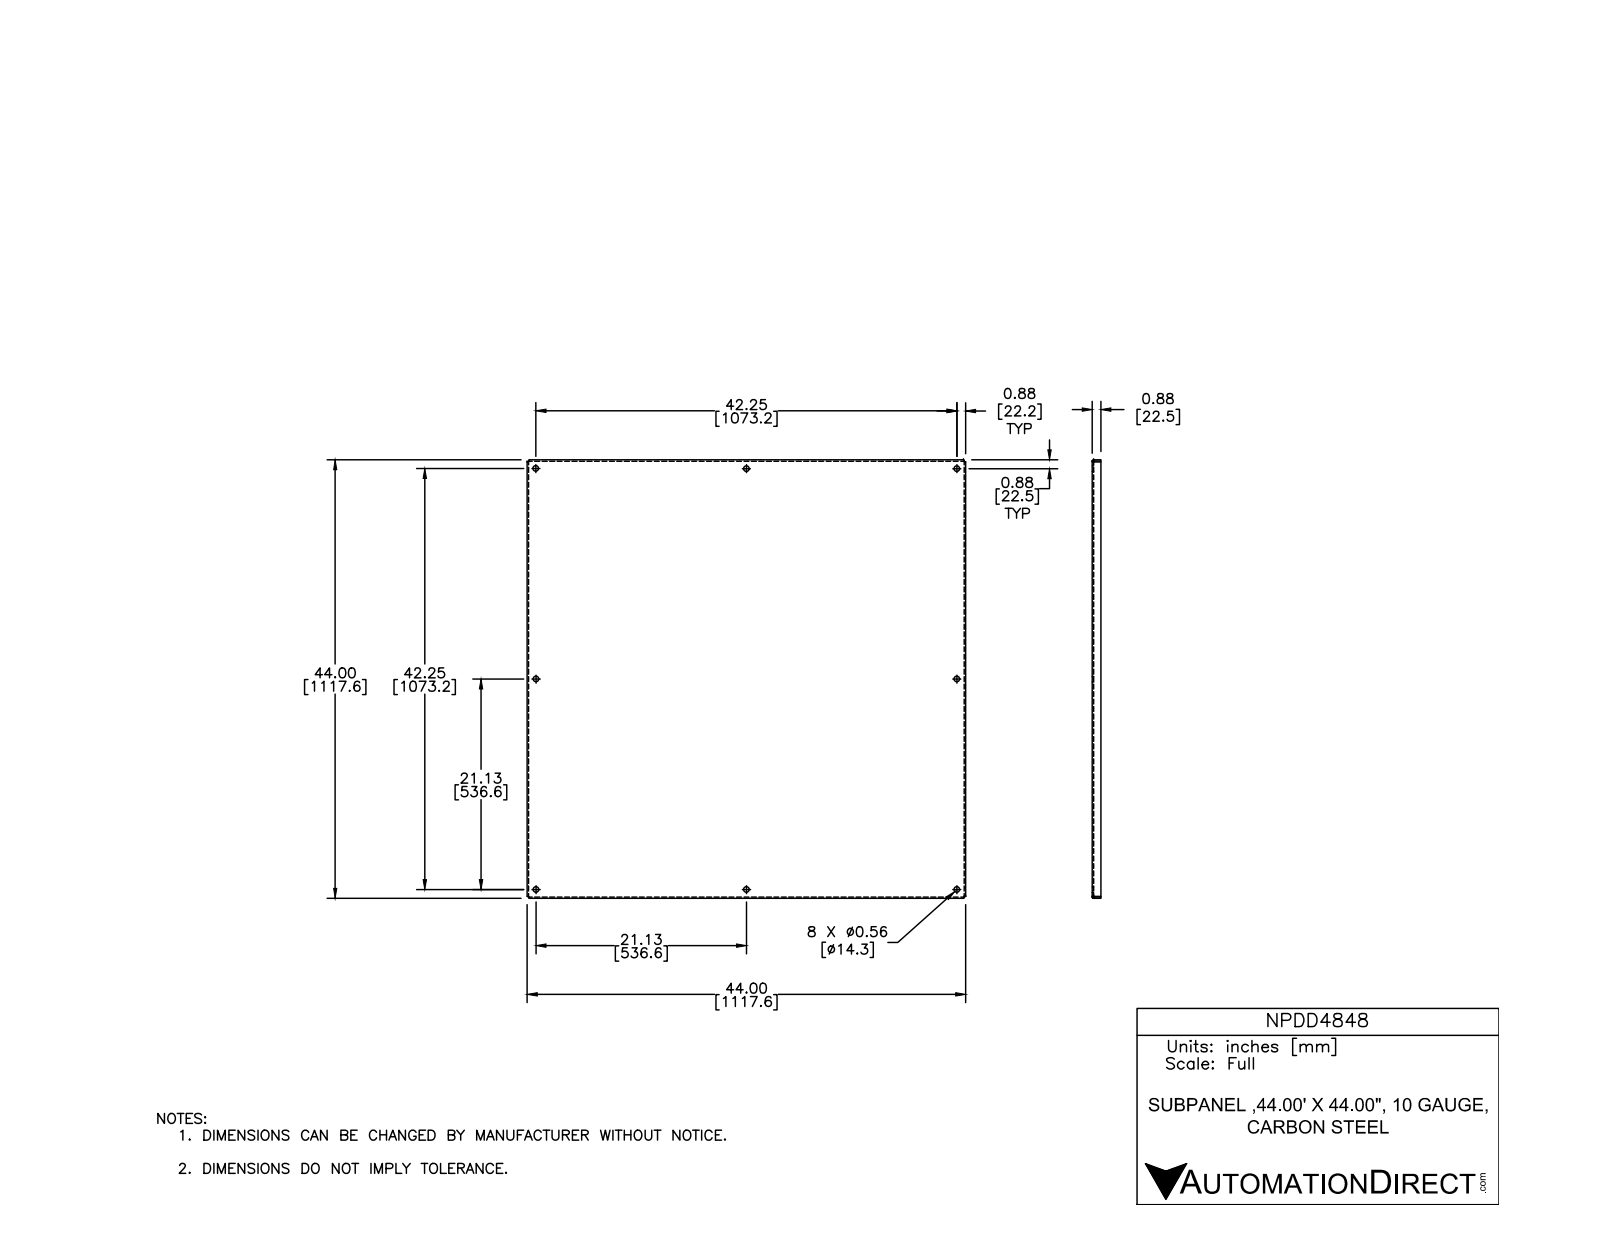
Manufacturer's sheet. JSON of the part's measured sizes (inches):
{"part_name": "NPDD4242-NPDD7272", "step_written_by": "Autodesk Inventor 2012 (AUTOMOTIVE_DESIGN)", "units": "inches", "bodies": {"solids": 1, "faces": 46, "planar": 22, "cylindrical": 16, "other": 8}, "overall_size": [44, 44, 0.875], "volume_in3": 257.2, "surface_area_in2": 4140, "round_holes": [[0.563, 8]], "partial_cylinders_radius": [[0.031, 4], [0.156, 4]], "face_to_face_distances": [0.125, 43.875, 44, 43.875, 43.75, 0.125, 43.75, 0.75, 0.875, 43.787], "hole_center_spacings": [47.237, 42.25, 21.125, 21.125, 29.875, 59.75, 29.875, 29.876]}
